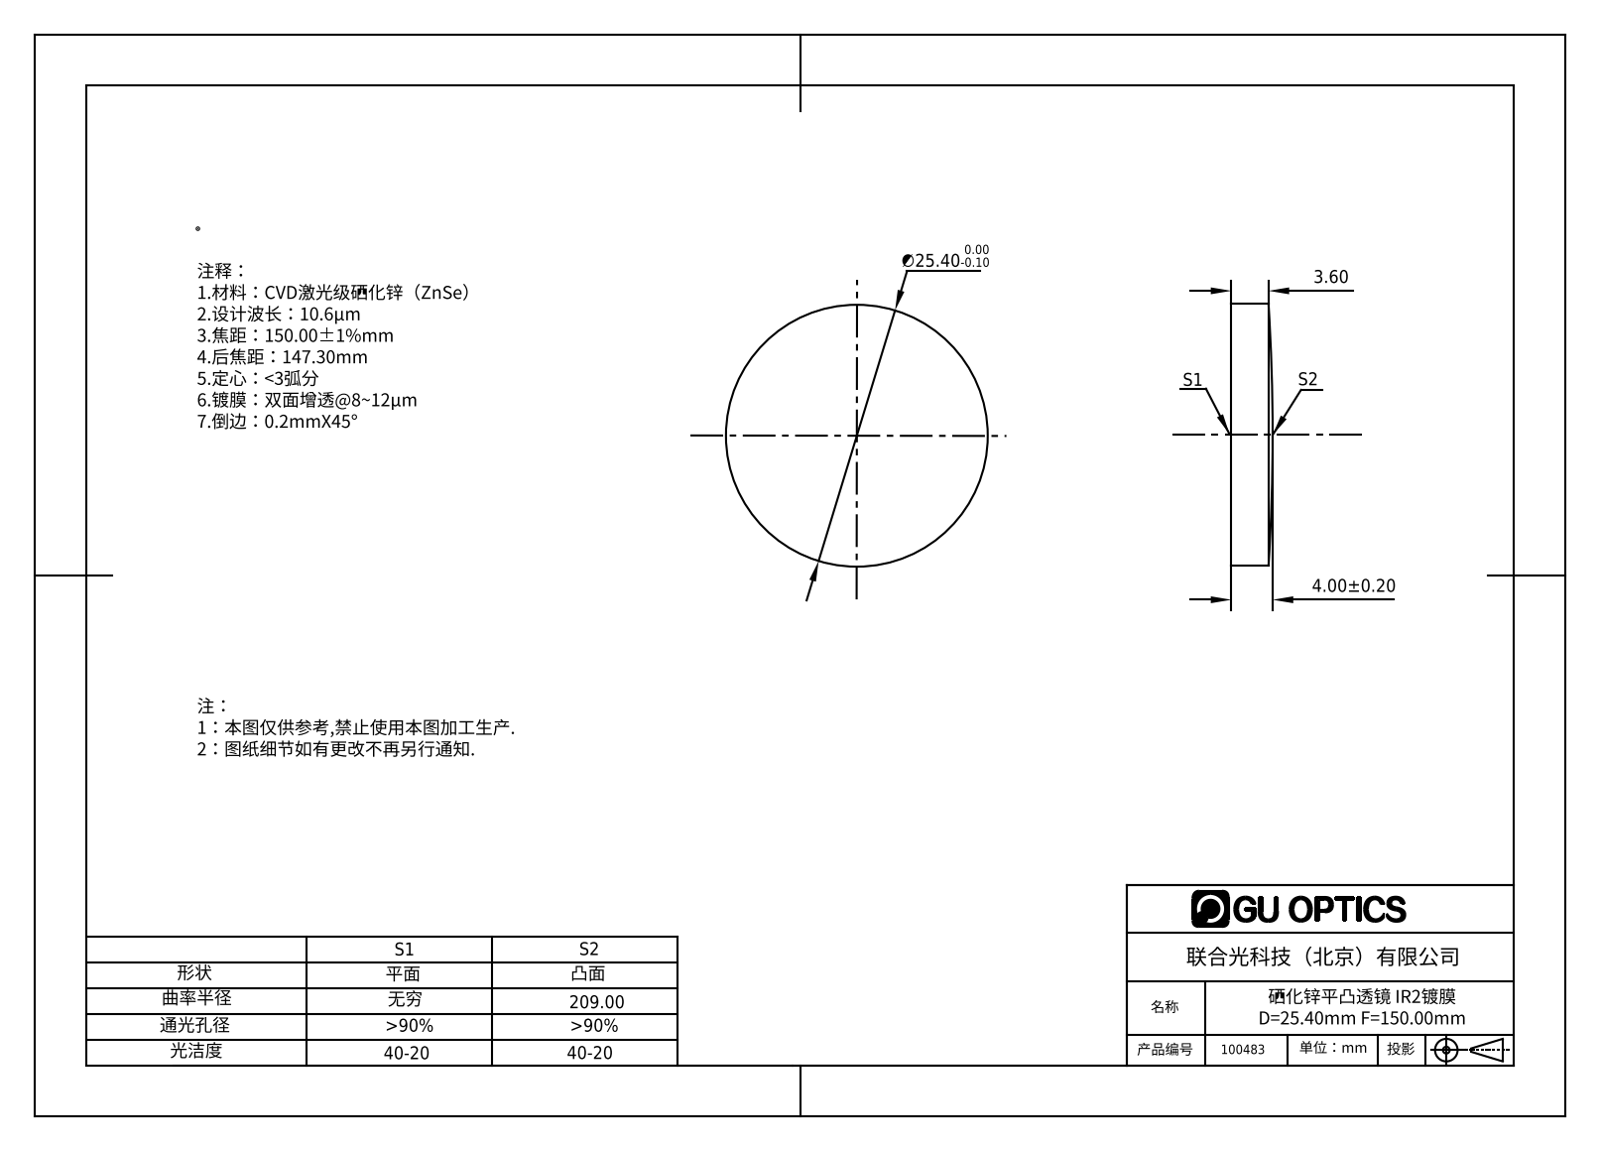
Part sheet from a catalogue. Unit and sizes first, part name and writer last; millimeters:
Units: millimetres
Overall size (bounding box): 25.4 × 25.4 × 4
Round bosses / shafts (diameter × count): ⌀25.4 ×1
Volume: 1 926 mm³ · Surface area: 1 301 mm²
Bodies: 1 solid, 5 faces (1 planar, 2 cylindrical, 2 other)
Part name (STEP PRODUCT): 100471
STEP written by: SolidWorks 2016 (AUTOMOTIVE_DESIGN)
